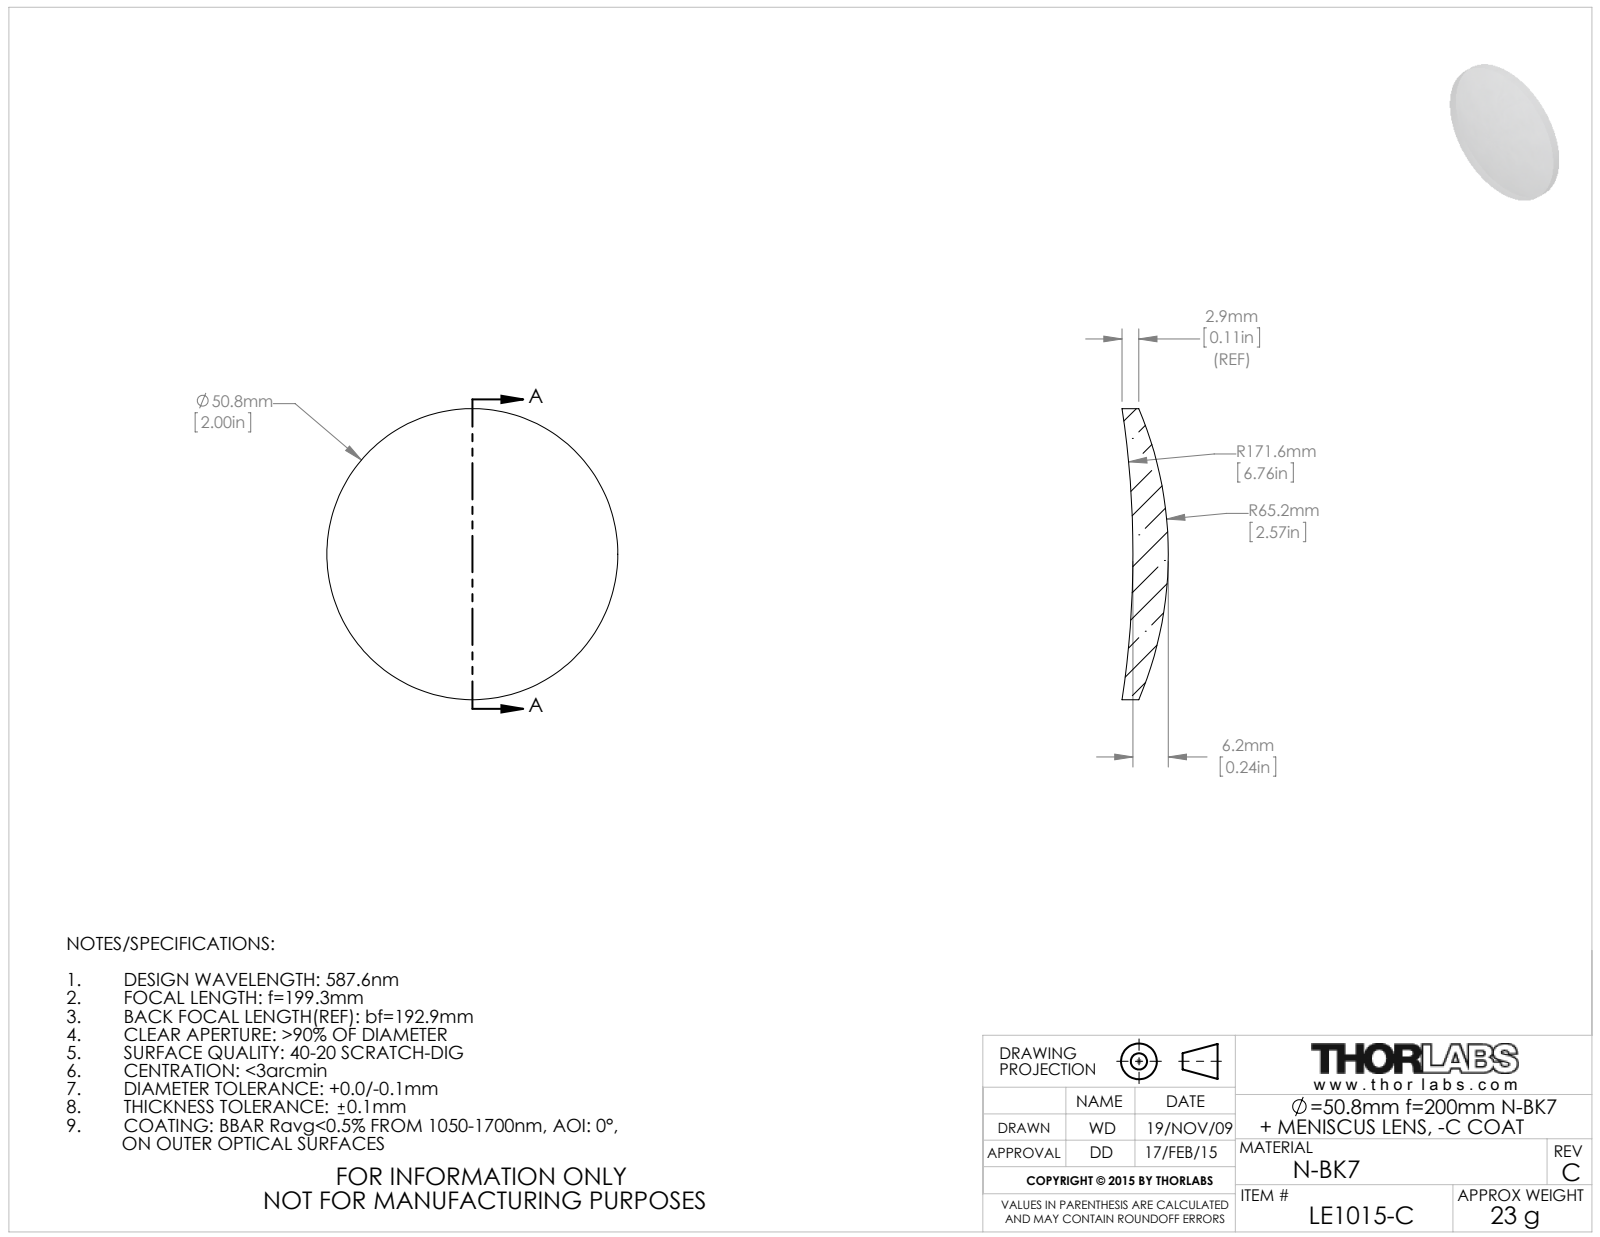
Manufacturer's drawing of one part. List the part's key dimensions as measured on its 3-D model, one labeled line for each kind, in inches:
Part name (STEP PRODUCT): 4862-E0W
STEP written by: SolidWorks 2009 (AUTOMOTIVE_DESIGN)
Units: inches
Bodies: 1 solid, 6 faces (0 planar, 2 cylindrical, 4 other)
Overall size (bounding box): 2 × 2 × 0.318
Volume: 0.567 in³ · Surface area: 7.152 in²
Round bosses / shafts (diameter × count): ⌀2 ×1
